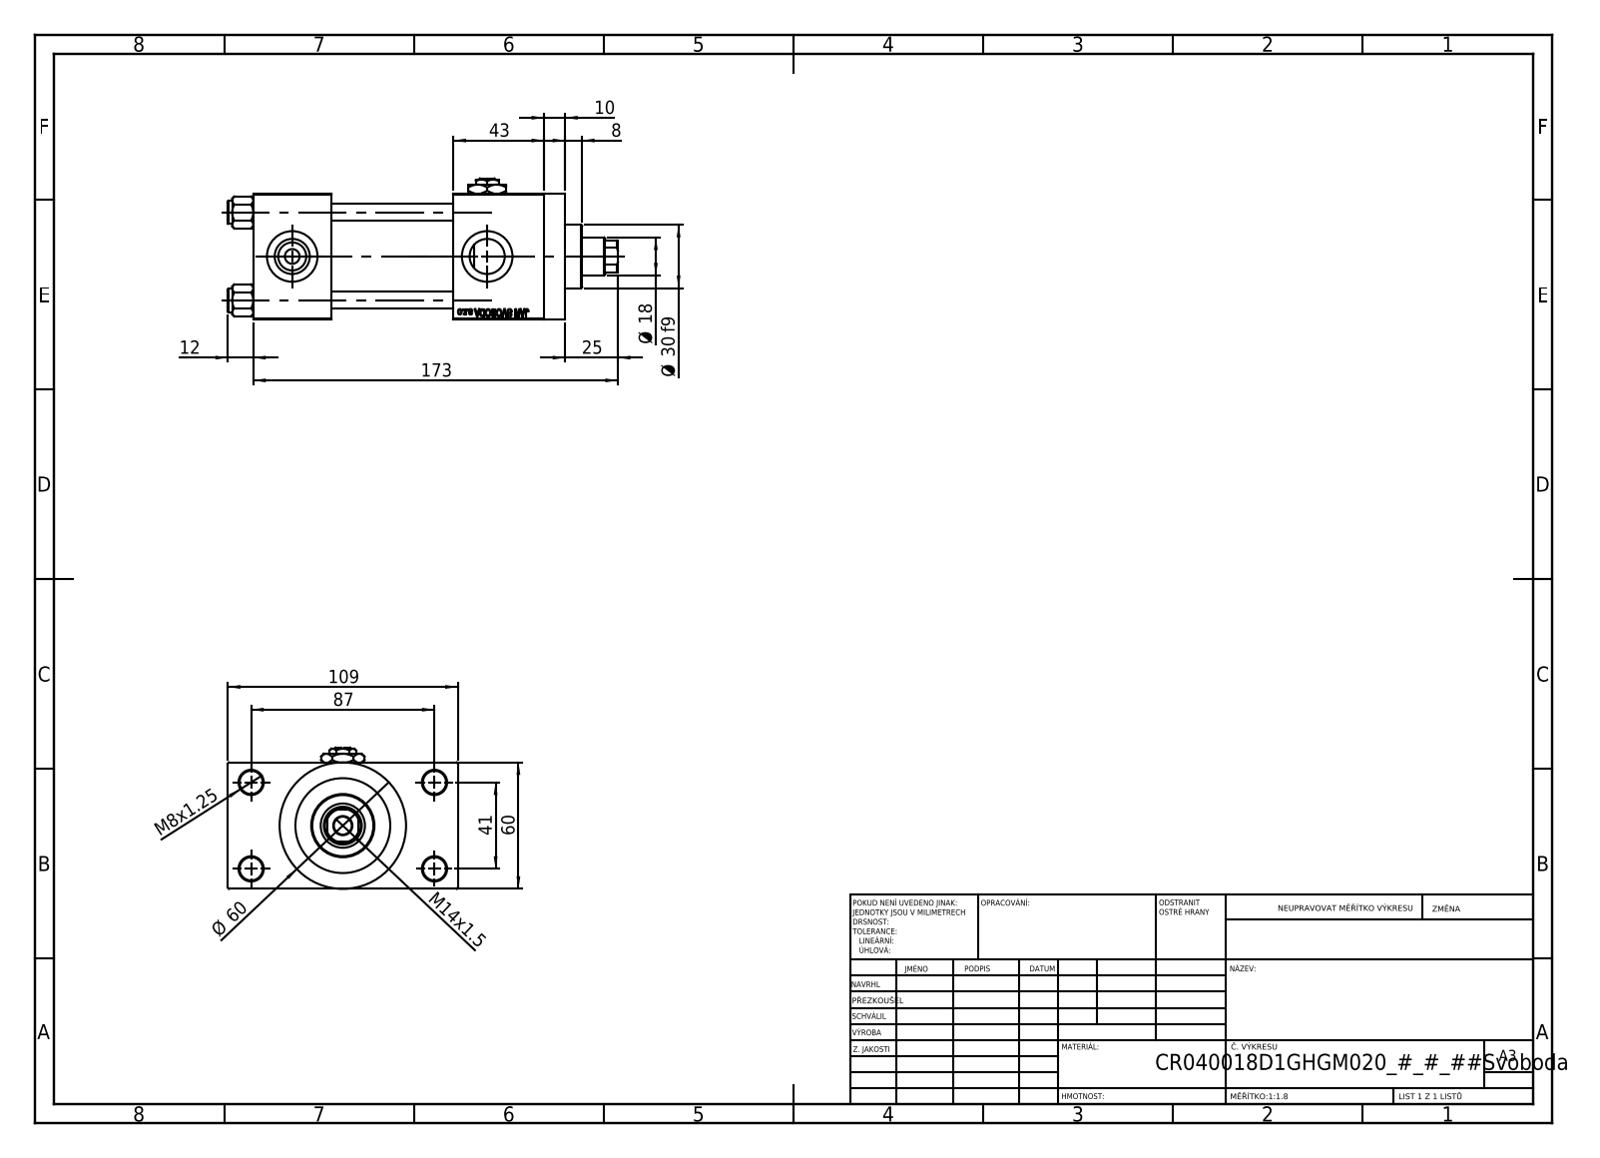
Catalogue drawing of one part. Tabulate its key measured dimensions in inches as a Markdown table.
| quantity | value |
| --- | --- |
| part name | V215CR_VCP_D; Zatka_pro_OIL_PORT; V215CR_D_Body; NUT_M5_D (+2 more) |
| STEP written by | SolidWorks 2019 (CONFIG_CONTROL_DESIGN) |
| units | inches |
| bodies | 12 solids, 1152 faces (522 planar, 92 cylindrical, 538 other) |
| overall size | 7.283 × 4.291 × 2.638 |
| volume | 31.25 in³ |
| surface area | 191.4 in² |
| round holes (diameter × count) | 0.315 × 4, 0.433 × 4, 0.656 × 3, 0.945 × 3, 0.276 × 2, 0.335 × 1, 0.709 × 1, 0.827 × 1, 1.22 × 1, 1.575 × 1, 1.772 × 1 |
| round bosses / shafts (diameter × count) | 0.433 × 4, 2.362 × 1, 1.811 × 1, 1.181 × 1 |
| partial cylindrical surfaces (radius × count) | 0.335 × 1 |
| main face-to-face distances | 2.362, 2.283, 0.965, 3.327, 1.457, 3.74, 1.693, 5.433, 3.976, 0.394 |
| hole center spacings | 0.892, 1.161, 1.642, 1.856, 1.893, 2.533, 3.011, 1.614 |
